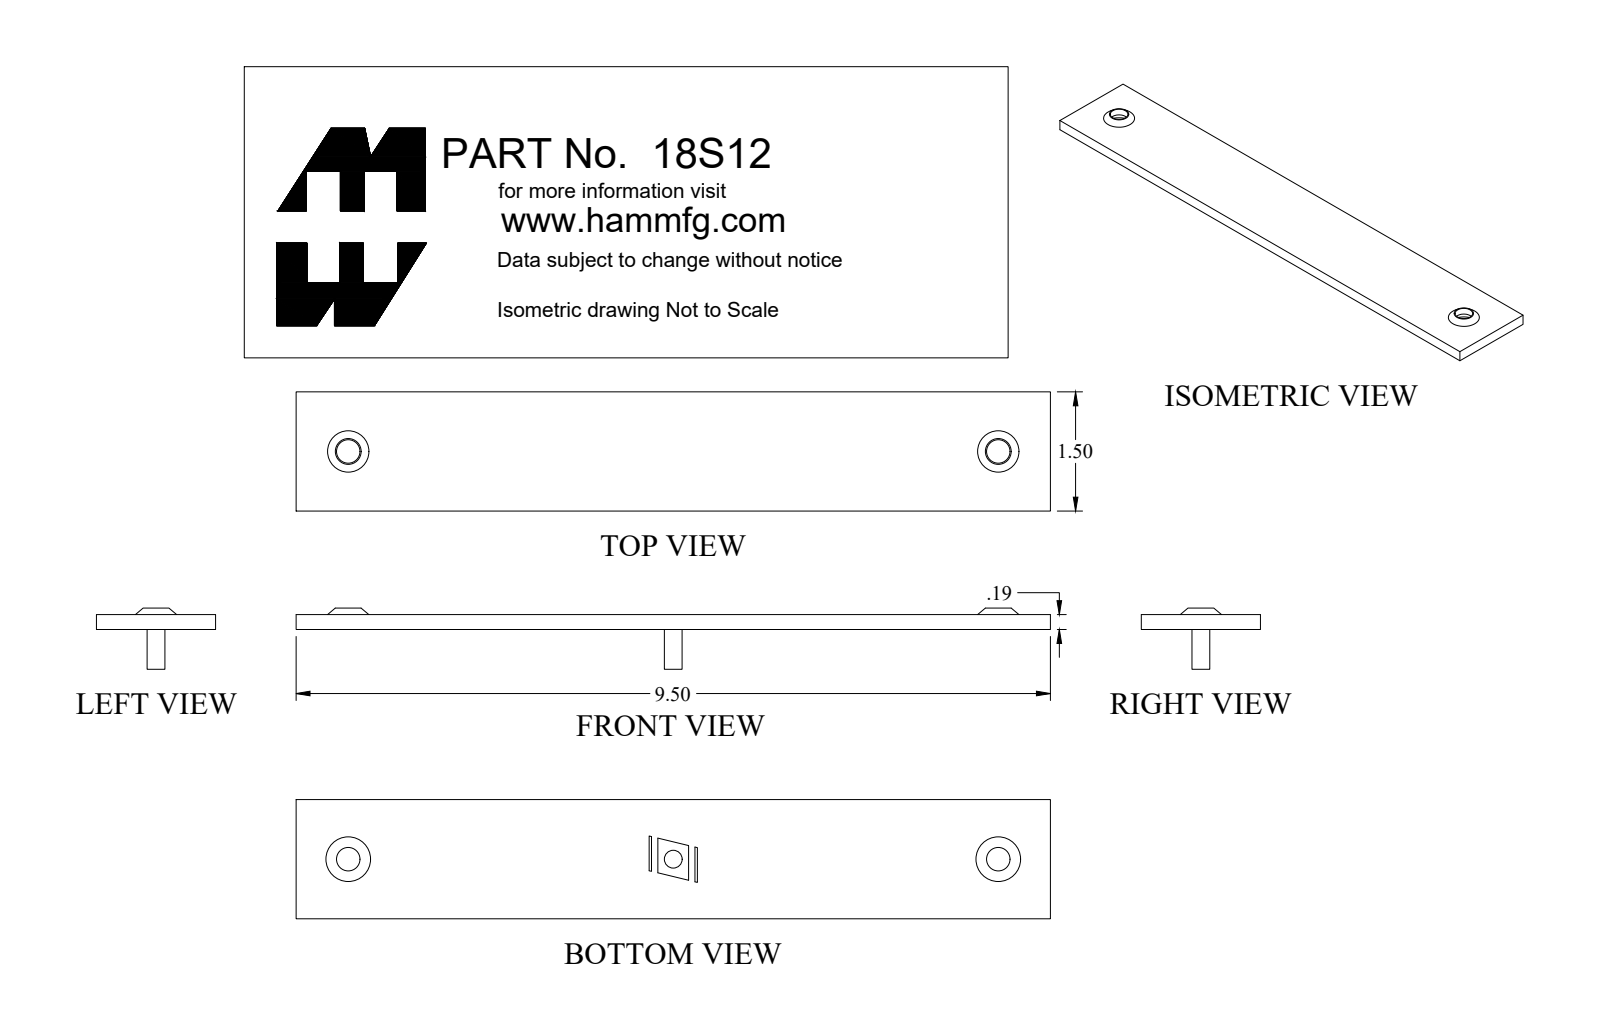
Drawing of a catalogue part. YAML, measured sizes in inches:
part_name: "18S12_Default"
step_written_by: "SolidWorks 2018 (CONFIG_CONTROL_DESIGN)"
units: inches
bodies: {solids: 1, faces: 20, planar: 8, cylindrical: 4, other: 8}
overall_size: [9.5, 1.5, 0.27]
volume: 2.641
surface_area: 32.85
round_holes:
  - {diameter: 0.296, count: 2}
face_to_face_distances: [0.188, 1.5, 9.5, 0.27, 0.082]
hole_center_spacings: [8.188]
